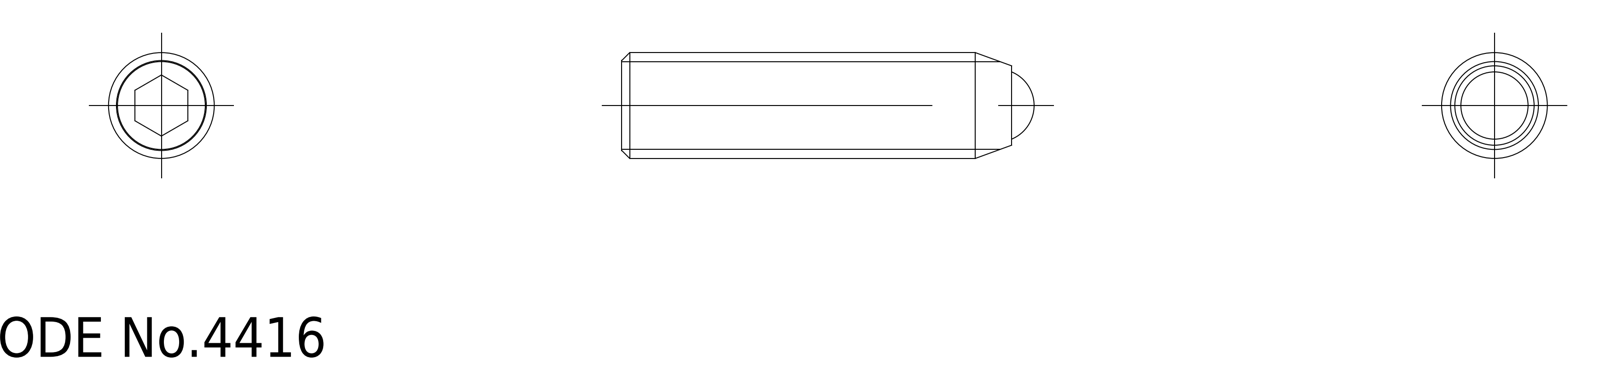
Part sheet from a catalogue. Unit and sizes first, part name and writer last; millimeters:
Units: millimetres
Overall size (bounding box): 31.2 × 8 × 8
Volume: 1 342 mm³ · Surface area: 1 064 mm²
Bodies: 2 solids, 20 faces (0 planar, 0 cylindrical, 20 other)
Part name (STEP PRODUCT): ball; SCSS_M8_30_R_19347_36
STEP written by: CADfix (AUTOMOTIVE_DESIGN)
